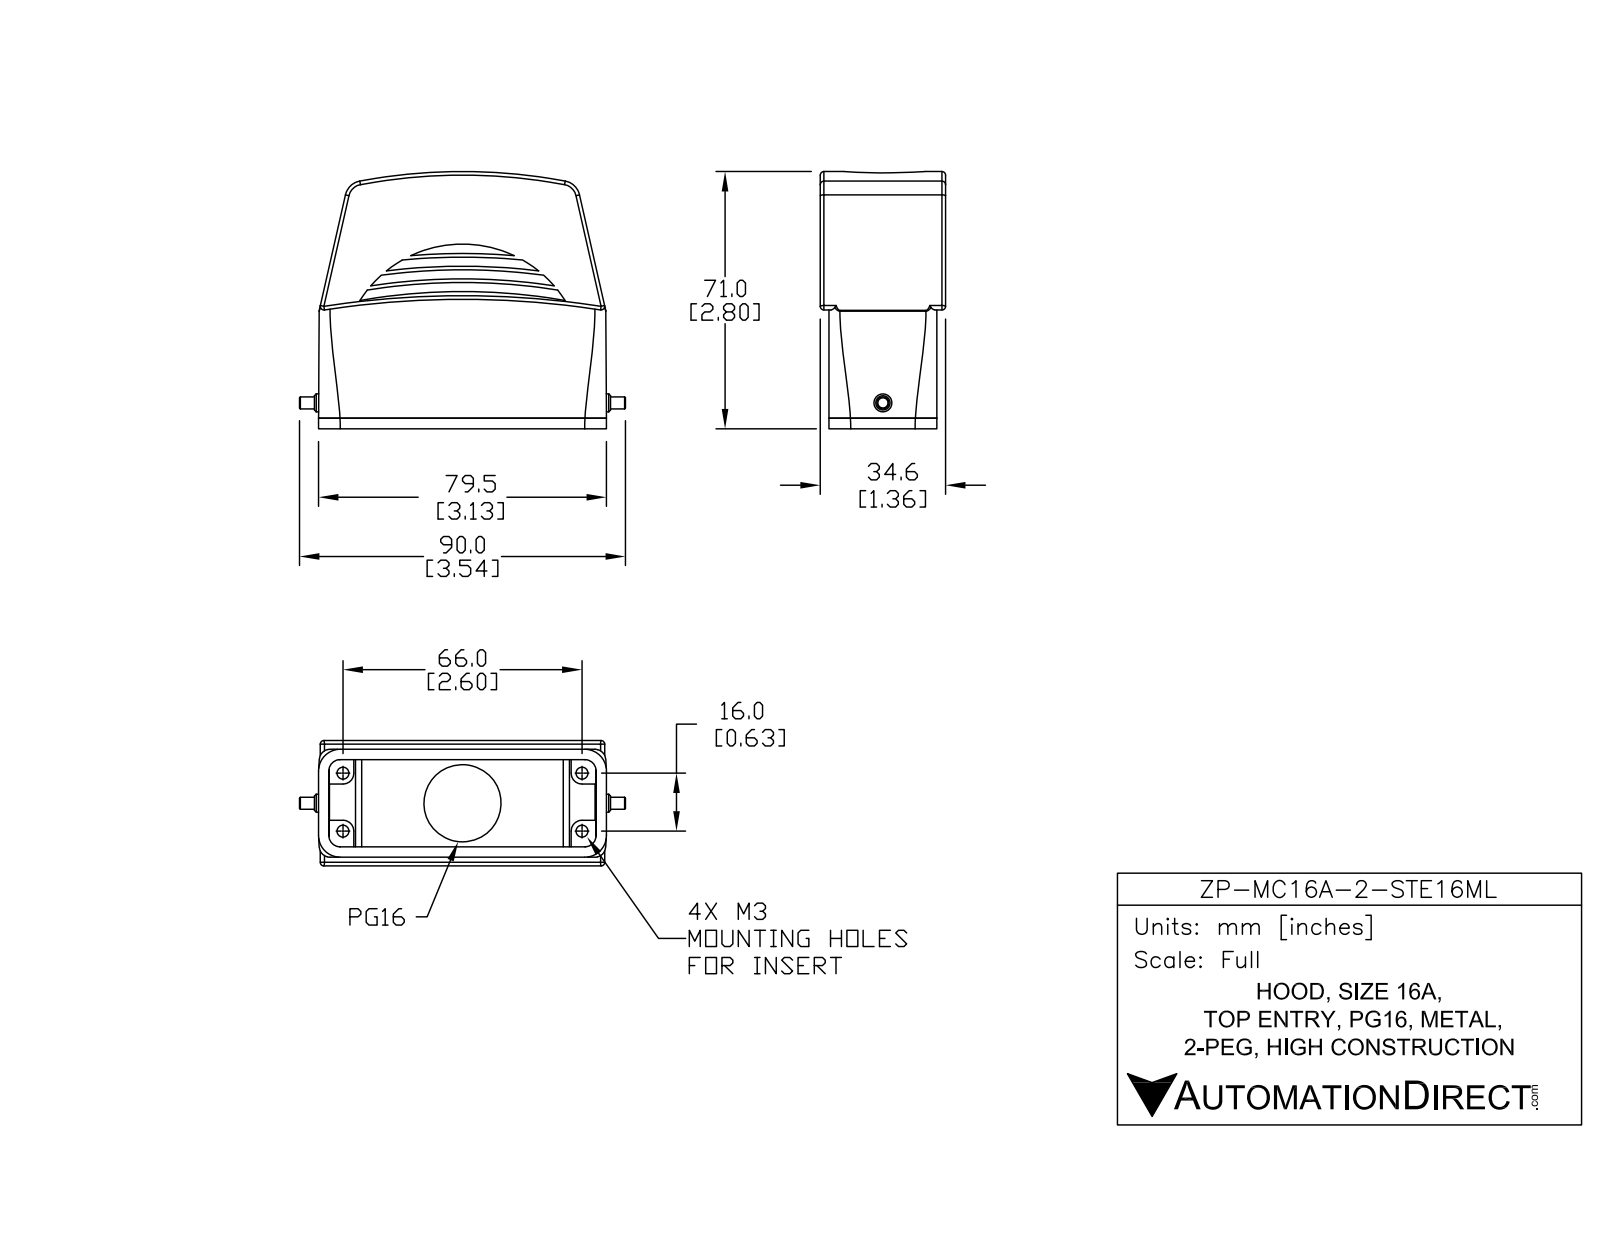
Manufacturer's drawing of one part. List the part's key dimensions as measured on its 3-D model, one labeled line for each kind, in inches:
Part name (STEP PRODUCT): ZP-MC16A-2-STE16ML
STEP written by: SolidWorks 2014 (AUTOMOTIVE_DESIGN)
Units: inches
Bodies: 2 solids, 174 faces (54 planar, 75 cylindrical, 45 other)
Overall size (bounding box): 3.543 × 2.795 × 1.362
Volume: 3.69 in³ · Surface area: 50.57 in²
Round holes (diameter × count): ⌀0.13 ×4, ⌀0.839 ×1
Round bosses / shafts (diameter × count): ⌀0.195 ×1, ⌀0.131 ×1
Partial cylindrical surfaces — rounded edges, fillets, slot ends (radius × count): R0.039 ×9, R0.118 ×4, R0.085 ×2, R0.197 ×2, R1.321 ×1, R5.929 ×1, R6.041 ×1, R6.478 ×1
Main face-to-face distances: 0.112, 1.06, 0.948, 0.095, 0.207, 1.155, 1.267, 1.172, 1.362, 1.352
Hole centre spacings: 0.63, 1.334, 1.34, 2.598, 2.674
